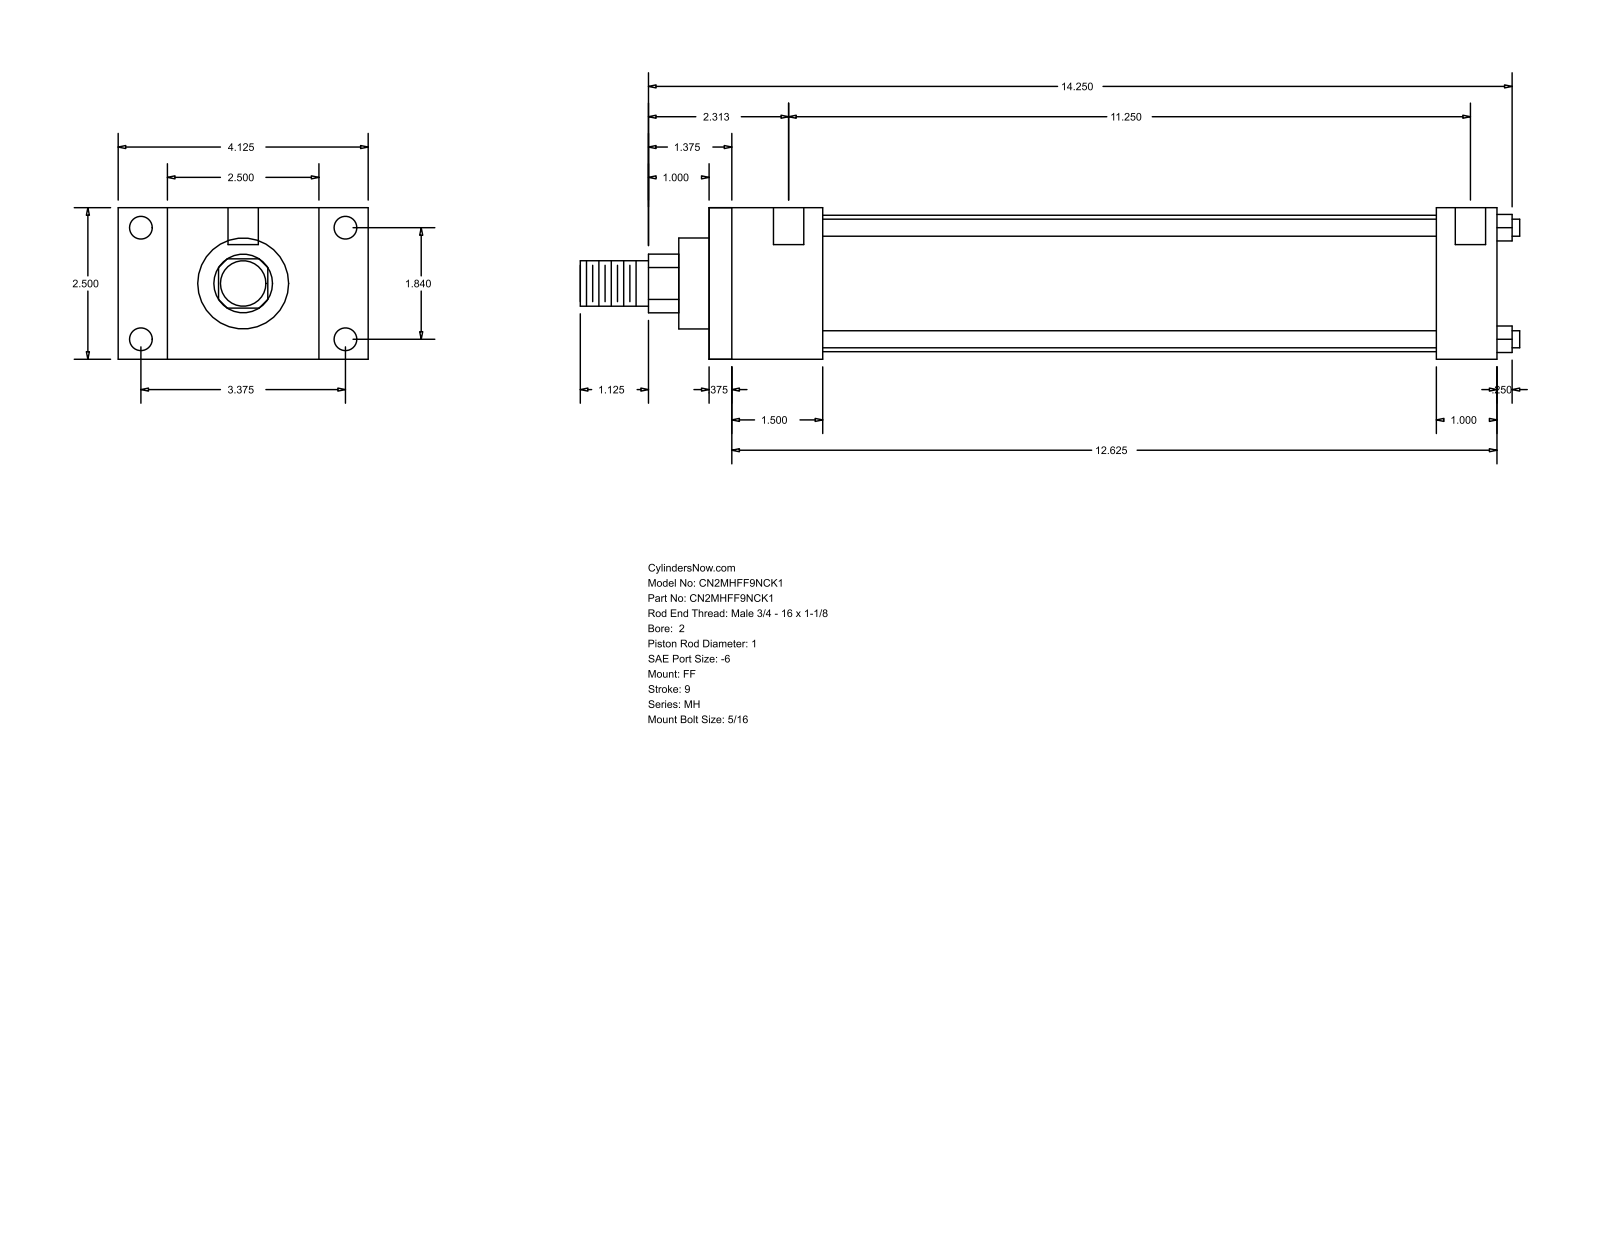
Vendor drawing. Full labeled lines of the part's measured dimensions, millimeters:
Part name (STEP PRODUCT): MH_FF__0200_1
STEP written by: GSSL Pune (CONFIG_CONTROL_DESIGN)
Units: millimetres
Bodies: 0 solids, 92 faces (64 planar, 28 cylindrical, 0 other)
Overall size (bounding box): 393.7 × 104.78 × 63.5
Round holes (diameter × count): ⌀5.56 ×4, ⌀9.53 ×4, ⌀12.7 ×2
Round bosses / shafts (diameter × count): ⌀7.14 ×4, ⌀57.15 ×1, ⌀38.1 ×1, ⌀25.4 ×1, ⌀19.05 ×1
Partial cylindrical surfaces — rounded edges, fillets, slot ends (radius × count): R12.29 ×1
Main face-to-face distances: 63.5, 330.2, 9.52, 320.68, 20.64, 25.4, 47.63, 304.8, 38.11, 295.28
Hole centre spacings: 46.74, 85.72, 97.63, 293.68, 3.17, 4.76, 285.75, 288.92
